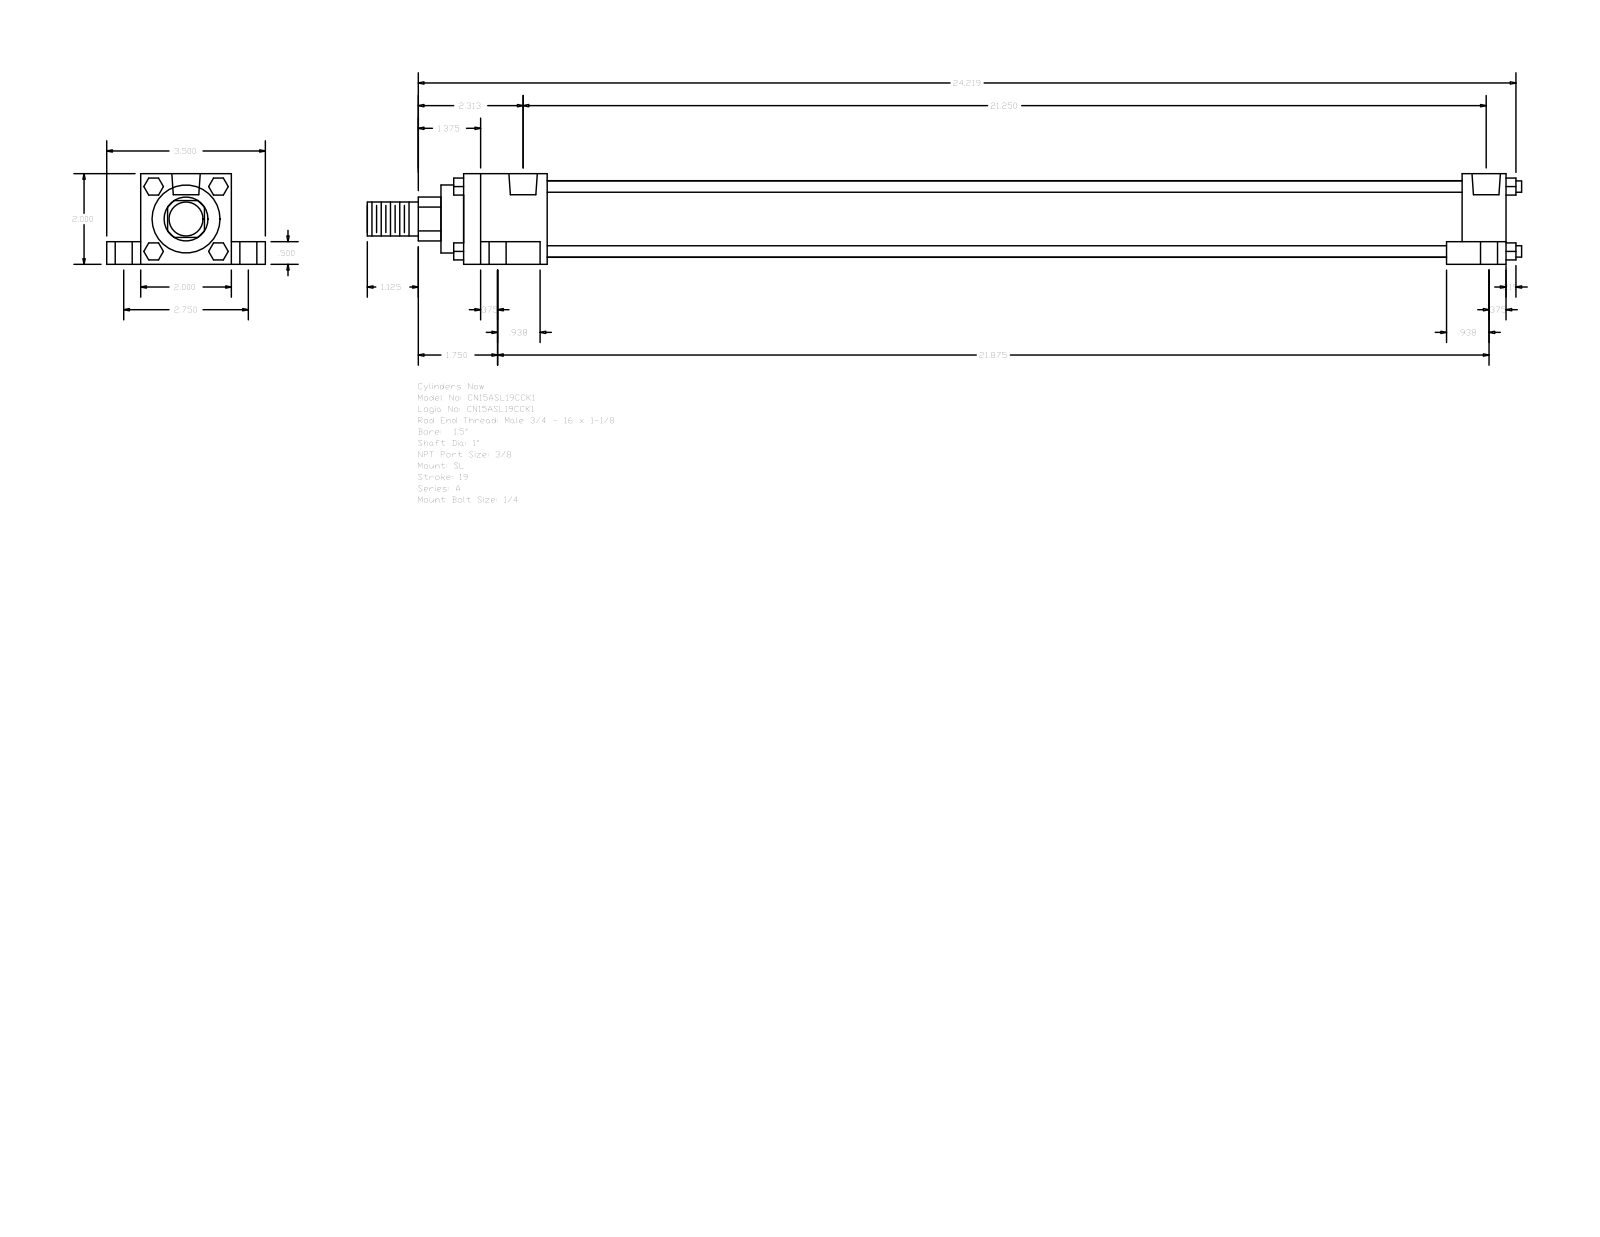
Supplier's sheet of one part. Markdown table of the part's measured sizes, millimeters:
| quantity | value |
| --- | --- |
| part name | A_SL__0150_1 |
| STEP written by | GSSL Pune (CONFIG_CONTROL_DESIGN) |
| units | millimeters |
| bodies | 0 solids, 148 faces (112 planar, 36 cylindrical, 0 other) |
| overall size | 646.91 × 88.9 × 50.8 |
| round holes (diameter × count) | 5.56 × 4, 9.53 × 4, 15.88 × 4, 15.93 × 2 |
| round bosses / shafts (diameter × count) | 6.35 × 4, 42.93 × 1, 38.1 × 1, 25.4 × 1, 19.05 × 1 |
| partial cylindrical surfaces (radius × count) | 12.29 × 1 |
| main face-to-face distances | 50.8, 12.7, 38.1, 19.05, 69.85, 9.52, 584.2, 33.34, 559.59, 24.61 |
| hole center spacings | 3.97, 34.96, 35.36, 37.73, 39.41, 69.84, 531.81, 535.78 |
